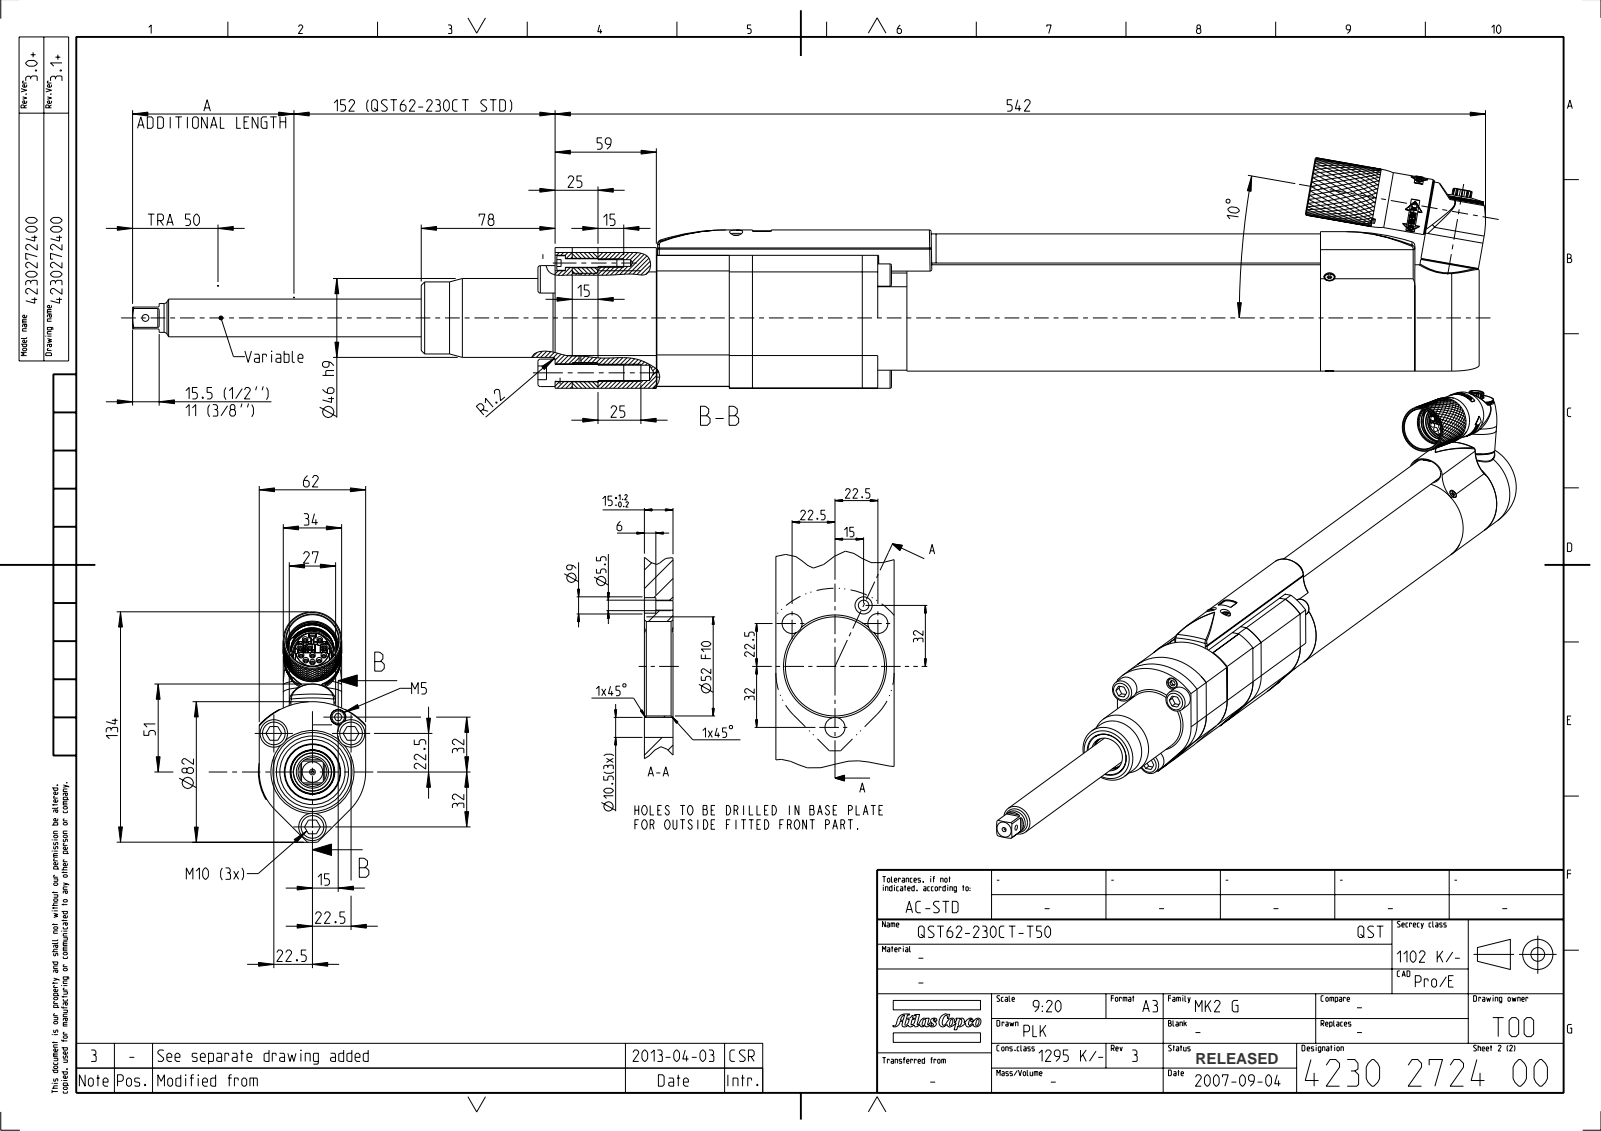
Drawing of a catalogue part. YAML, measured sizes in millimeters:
part_name: "QST62_REARCOVER_02; QST_CONNECTOR_02; QST62_230_CT_BODY; QST62_SPACER_01 (+3 more)"
step_written_by: "PRO/ENGINEER BY PARAMETRIC TECHNOLOGY CORPORATION, 2012420 (CONFIG_CONTROL_DESIGN)"
units: millimeters
bodies: {solids: 6, faces: 3045, planar: 1189, cylindrical: 965, other: 891}
overall_size: [694.18, 134.4, 62]
volume: 1177000
surface_area: 401012
round_holes:
  - {diameter: 4.5, count: 8}
  - {diameter: 3.3, count: 7}
  - {diameter: 3.92, count: 4}
  - {diameter: 5.5, count: 4}
  - {diameter: 7.5, count: 4}
  - {diameter: 9, count: 4}
  - {diameter: 1.9, count: 3}
  - {diameter: 3.5, count: 3}
  - {diameter: 6.92, count: 3}
  - {diameter: 8.5, count: 3}
  - {diameter: 8.92, count: 3}
  - {diameter: 10.3, count: 3}
round_bosses_or_shafts:
  - {diameter: 5, count: 5}
  - {diameter: 2.5, count: 5}
  - {diameter: 8, count: 4}
  - {diameter: 3, count: 4}
  - {diameter: 34, count: 3}
  - {diameter: 16, count: 3}
  - {diameter: 13, count: 3}
  - {diameter: 10, count: 3}
partial_cylinders:
  - {radius: 0.5, count: 45}
  - {radius: 0.2, count: 12}
  - {radius: 0.29, count: 12}
  - {radius: 0.51, count: 12}
  - {radius: 1, count: 7}
  - {radius: 0.8, count: 6}
  - {radius: 2, count: 5}
  - {radius: 0.68, count: 4}
face_to_face_distances: [62, 15, 3.5, 34, 476, 25, 250.5, 10, 513.5, 528.5]
hole_center_spacings: [22.5, 20.24, 14.79, 16.7, 23.1, 23.11, 28.92, 39.2]
